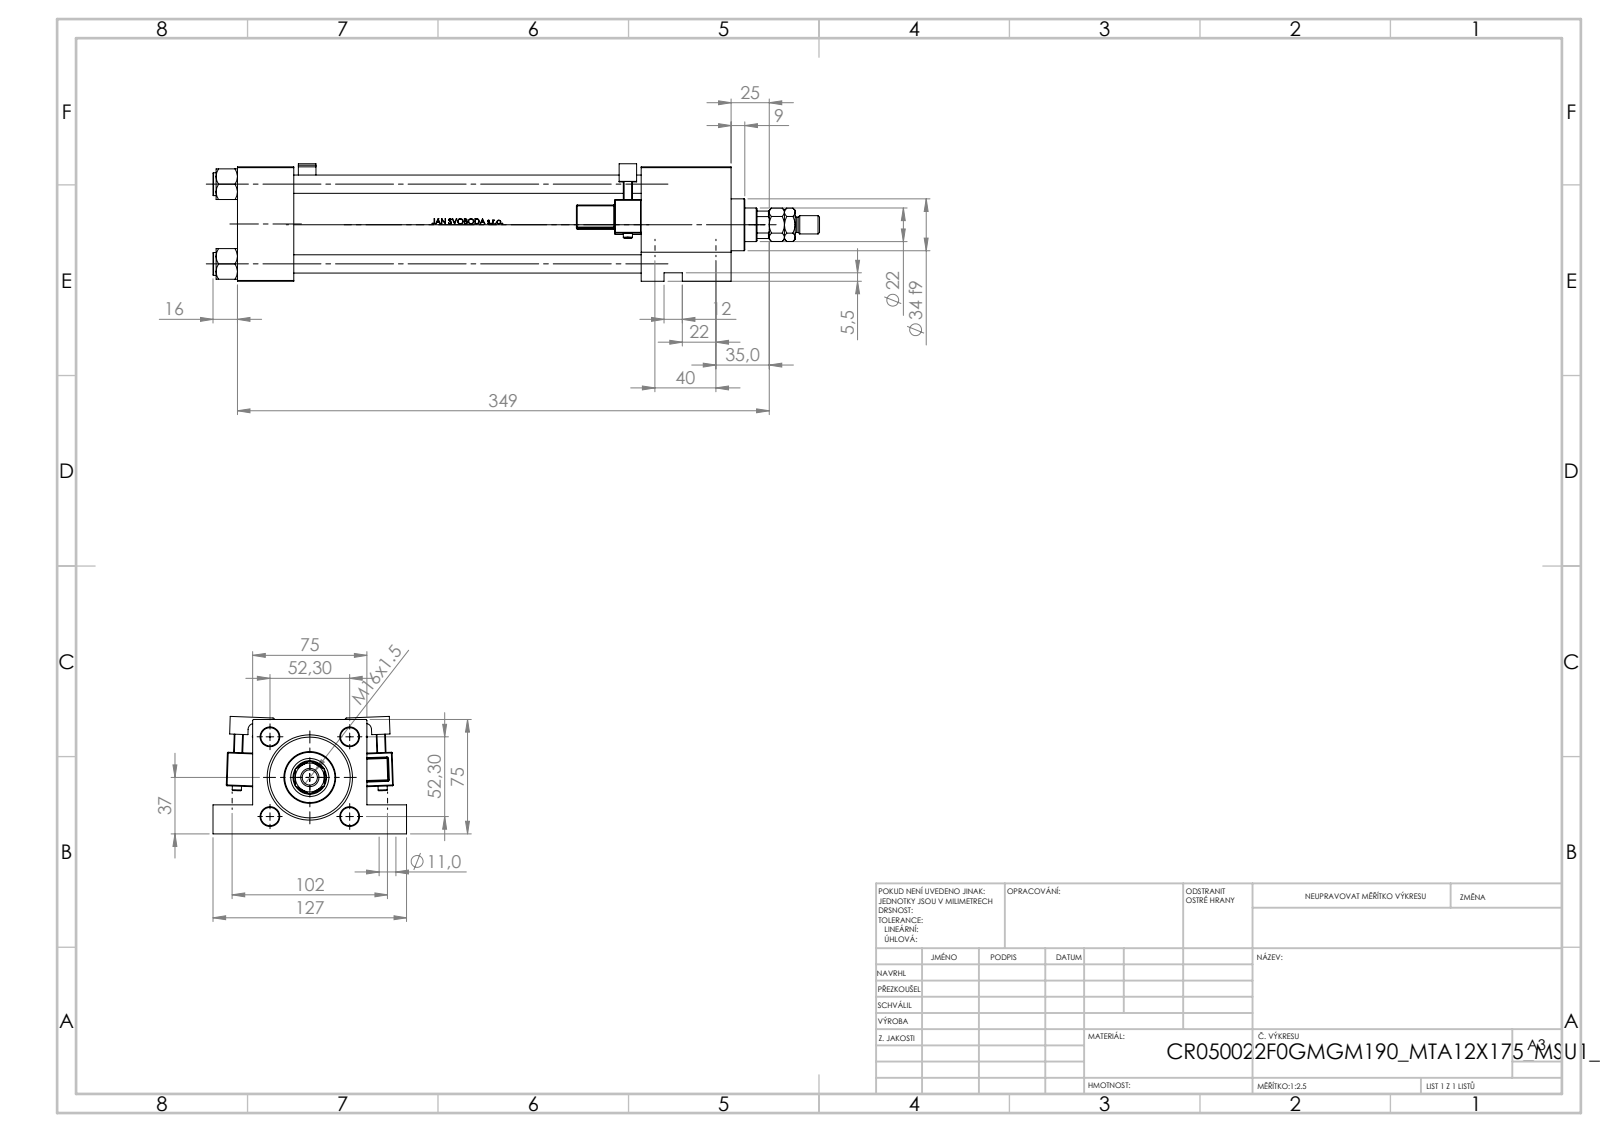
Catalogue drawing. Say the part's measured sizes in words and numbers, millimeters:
The part is named "V215CR_VCP_F; V215_VC_A; V215CR_MSU; V215CR_F_Body (+3 more)". Its 3-D file was written by "SolidWorks 2019 (CONFIG_CONTROL_DESIGN)". It is 14 solids with 1306 faces: 510 planar, 190 cylindrical and 606 other. Overall it measures 398 by 127 by 77.03 millimeters. Its volume is 981 269 cubic millimeters and its surface area 264 934 square millimeters. Round holes: 4 of diameter 11, 4 of diameter 12, 2 of diameter 7, 2 of diameter 30, 1 of diameter 10.5, 1 of diameter 17, 1 of diameter 20.96, 1 of diameter 22, 1 of diameter 25, 1 of diameter 41, 1 of diameter 50, 1 of diameter 53. Round bosses or shafts: 4 of diameter 15, 2 of diameter 6, 1 of diameter 56, 1 of diameter 34, 1 of diameter 12, 1 of diameter 10. Partial cylindrical surfaces (rounded edges, fillets, slot ends): 48 of radius 0.5, 2 of radius 1, 2 of radius 2.5, 2 of radius 4, 1 of radius 10.5. The main face-to-face distances are 75, 37, 324, 287, 265, 228, 59, 19, 56, 295.3. The hole center spacings are 52.3, 36.63, 37.34, 40, 73.96, 102, 109.56, 263.5.
